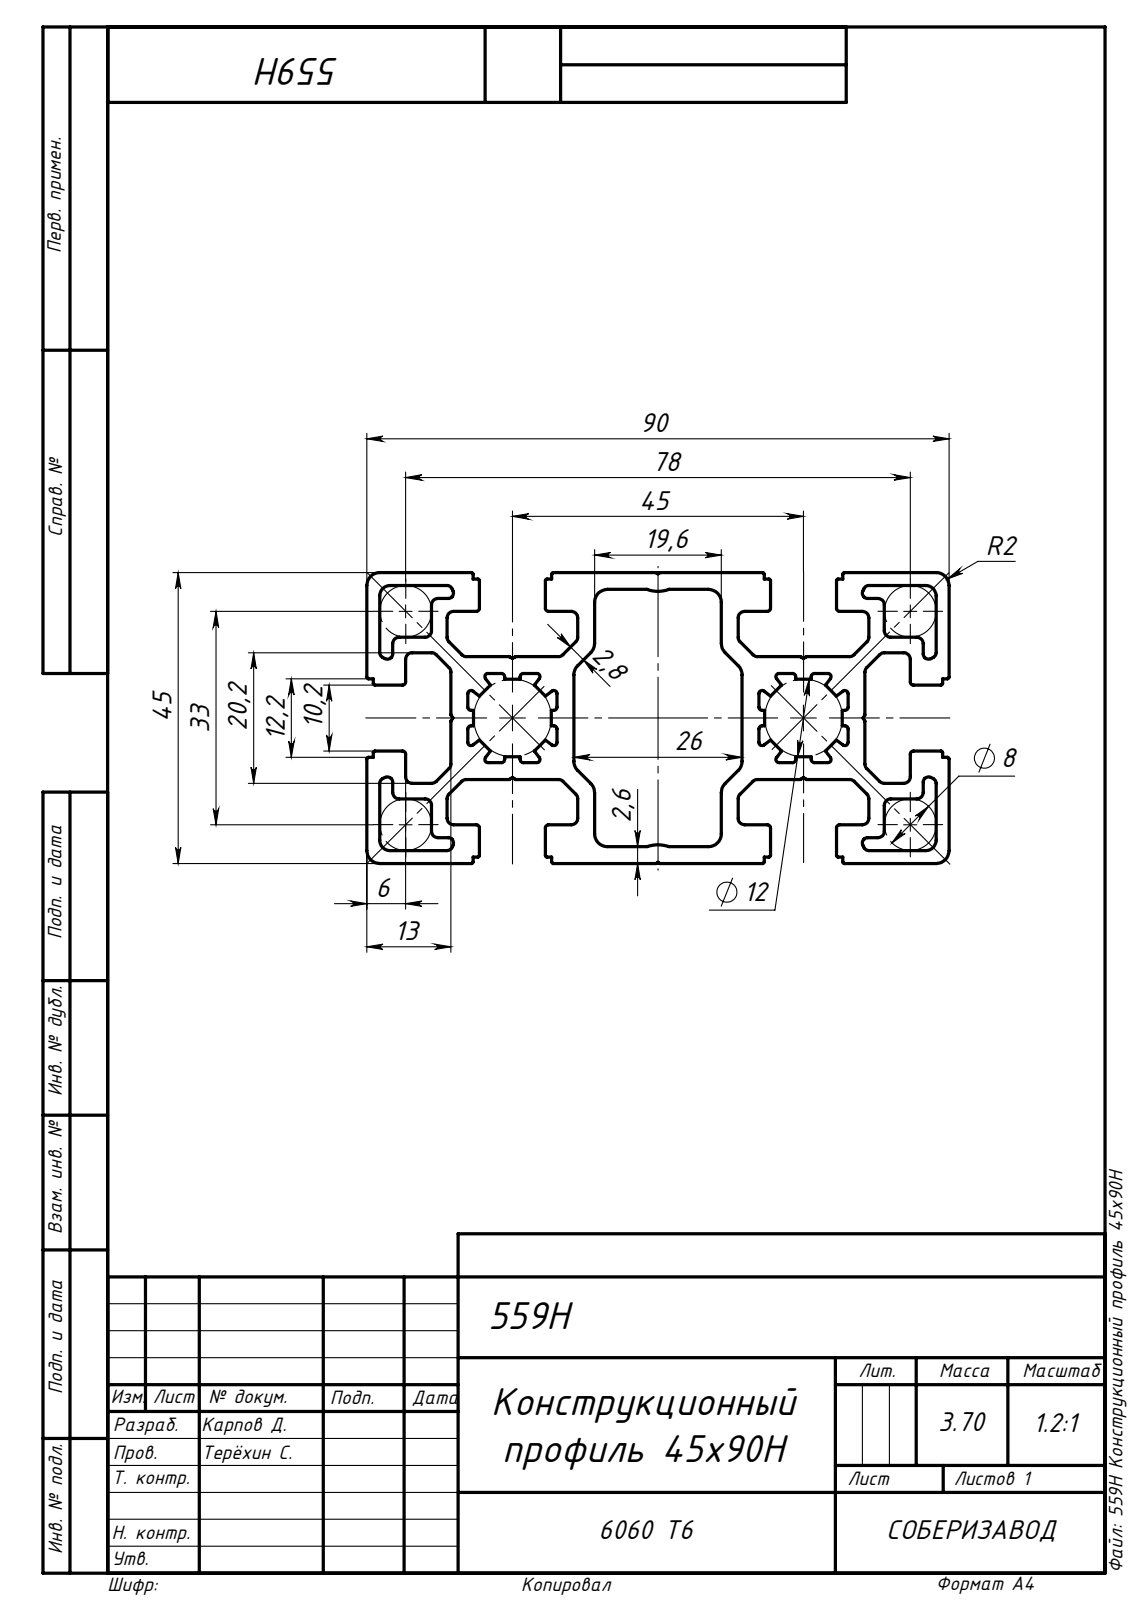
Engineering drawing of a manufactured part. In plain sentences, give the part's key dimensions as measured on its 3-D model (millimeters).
Its 3-D file was written by "SolidWorks 2019 (AUTOMOTIVE_DESIGN)". It is 1 solid with 426 faces: 232 planar, 194 cylindrical and 0 other. Overall it measures 1000 by 90 by 45 millimeters. Its volume is 1 371 000 cubic millimeters and its surface area 933 356 square millimeters. Partial cylindrical surfaces (rounded edges, fillets, slot ends): 48 of radius 1, 44 of radius 0.5, 40 of radius 0.25, 24 of radius 0.8, 16 of radius 2, 4 of radius 1.6, 2 of radius 5. The main face-to-face distances are 45, 13, 32, 30, 4, 2, 11, 7.4, 26, 2.6.
